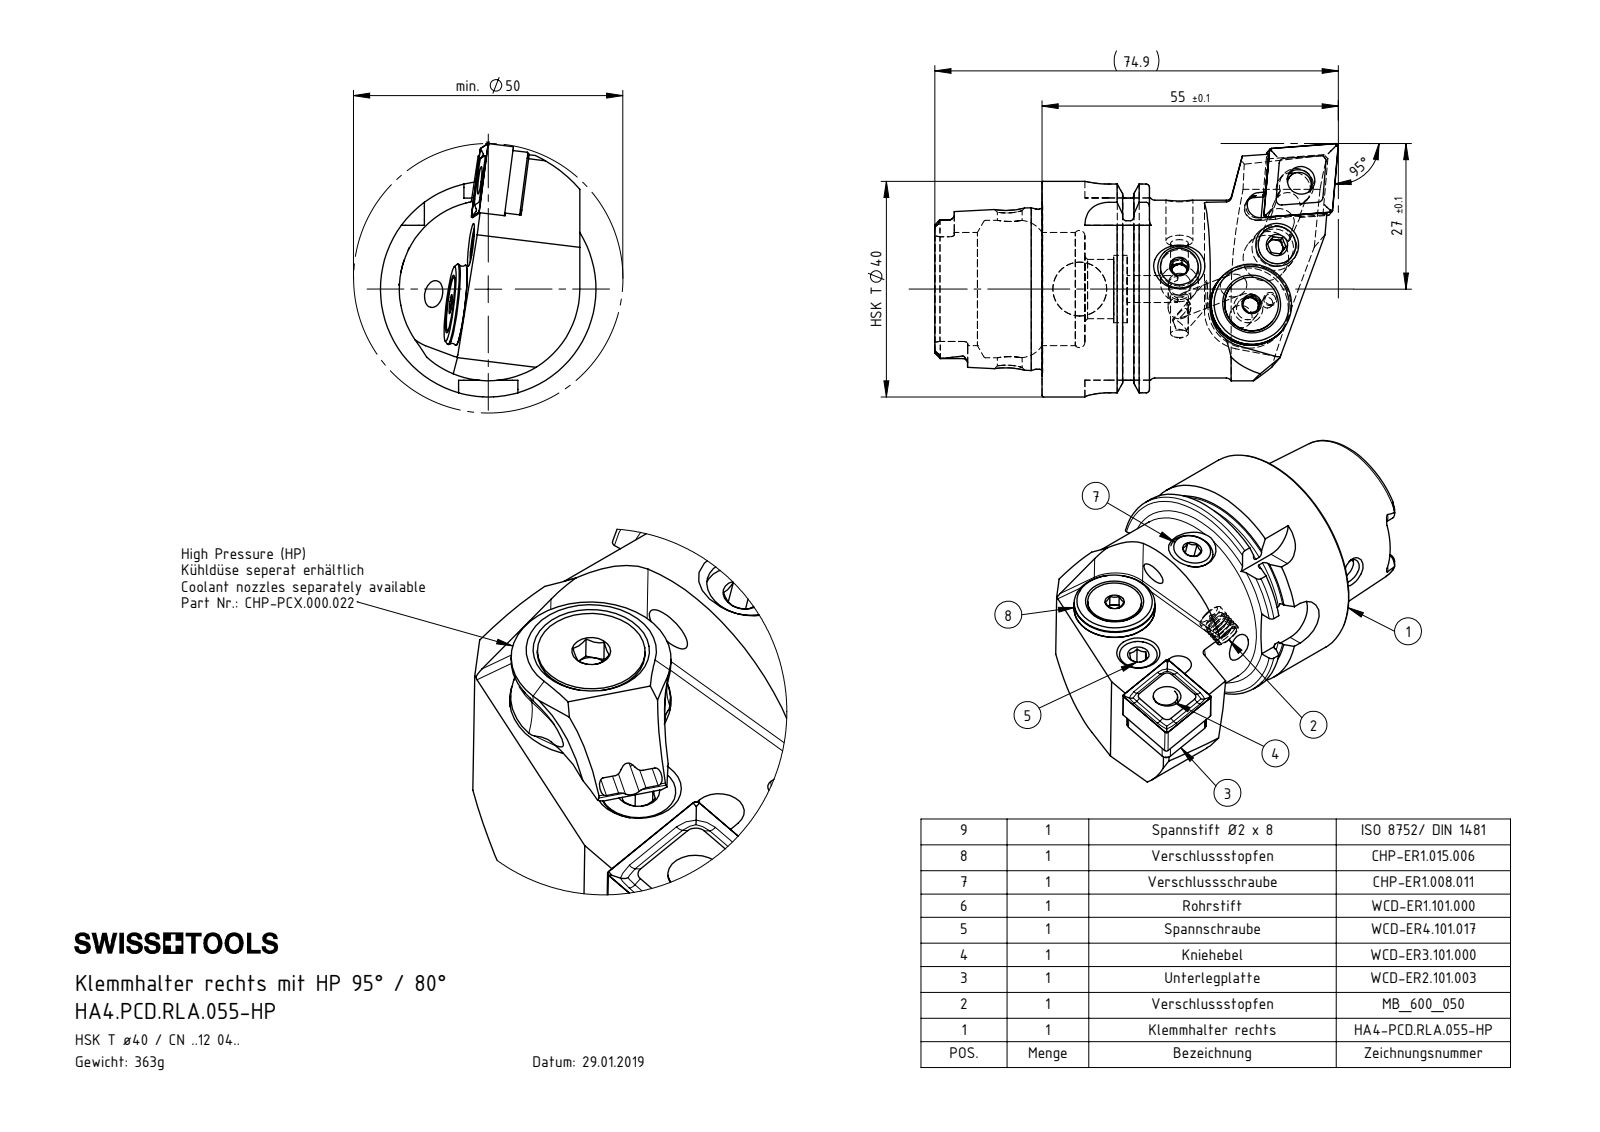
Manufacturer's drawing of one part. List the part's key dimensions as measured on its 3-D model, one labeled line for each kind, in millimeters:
Part name (STEP PRODUCT): DIN 7991 - M5x15; HA4.PCD.RLA.055-HP; CHP-ER1.015.006_A; CHP-ER1.008.011_A (+8 more)
STEP written by: SolidWorks 2017 (AUTOMOTIVE_DESIGN)
Units: millimetres
Bodies: 13 solids, 540 faces (167 planar, 148 cylindrical, 225 other)
Overall size (bounding box): 74.9 × 47 × 40
Volume: 45 339 mm³ · Surface area: 19 004 mm²
Round holes (diameter × count): ⌀4.2 ×3, ⌀3.3 ×2, ⌀5 ×2, ⌀7 ×2, ⌀1.2 ×1, ⌀2 ×1, ⌀2.5 ×1, ⌀3 ×1, ⌀4 ×1, ⌀4.6 ×1, ⌀5.16 ×1, ⌀5.2 ×1
Round bosses / shafts (diameter × count): ⌀8 ×2, ⌀5 ×2, ⌀40 ×1, ⌀34.75 ×1, ⌀33 ×1, ⌀29.71 ×1, ⌀15 ×1, ⌀13.4 ×1
Partial cylindrical surfaces — rounded edges, fillets, slot ends (radius × count): R0.9 ×6, R0.4 ×4, R1 ×4, R1.88 ×4, R4.5 ×4, R0.5 ×2, R2.5 ×2, R2.1 ×1
Main face-to-face distances: 4.46, 4.5, 7.95, 19.95, 12, 3.14, 3.18, 7.64, 19.9, 27.85
Hole centre spacings: 4.51, 9.67, 12.41, 25.19, 25.25, 4.5, 4.52, 12.8
